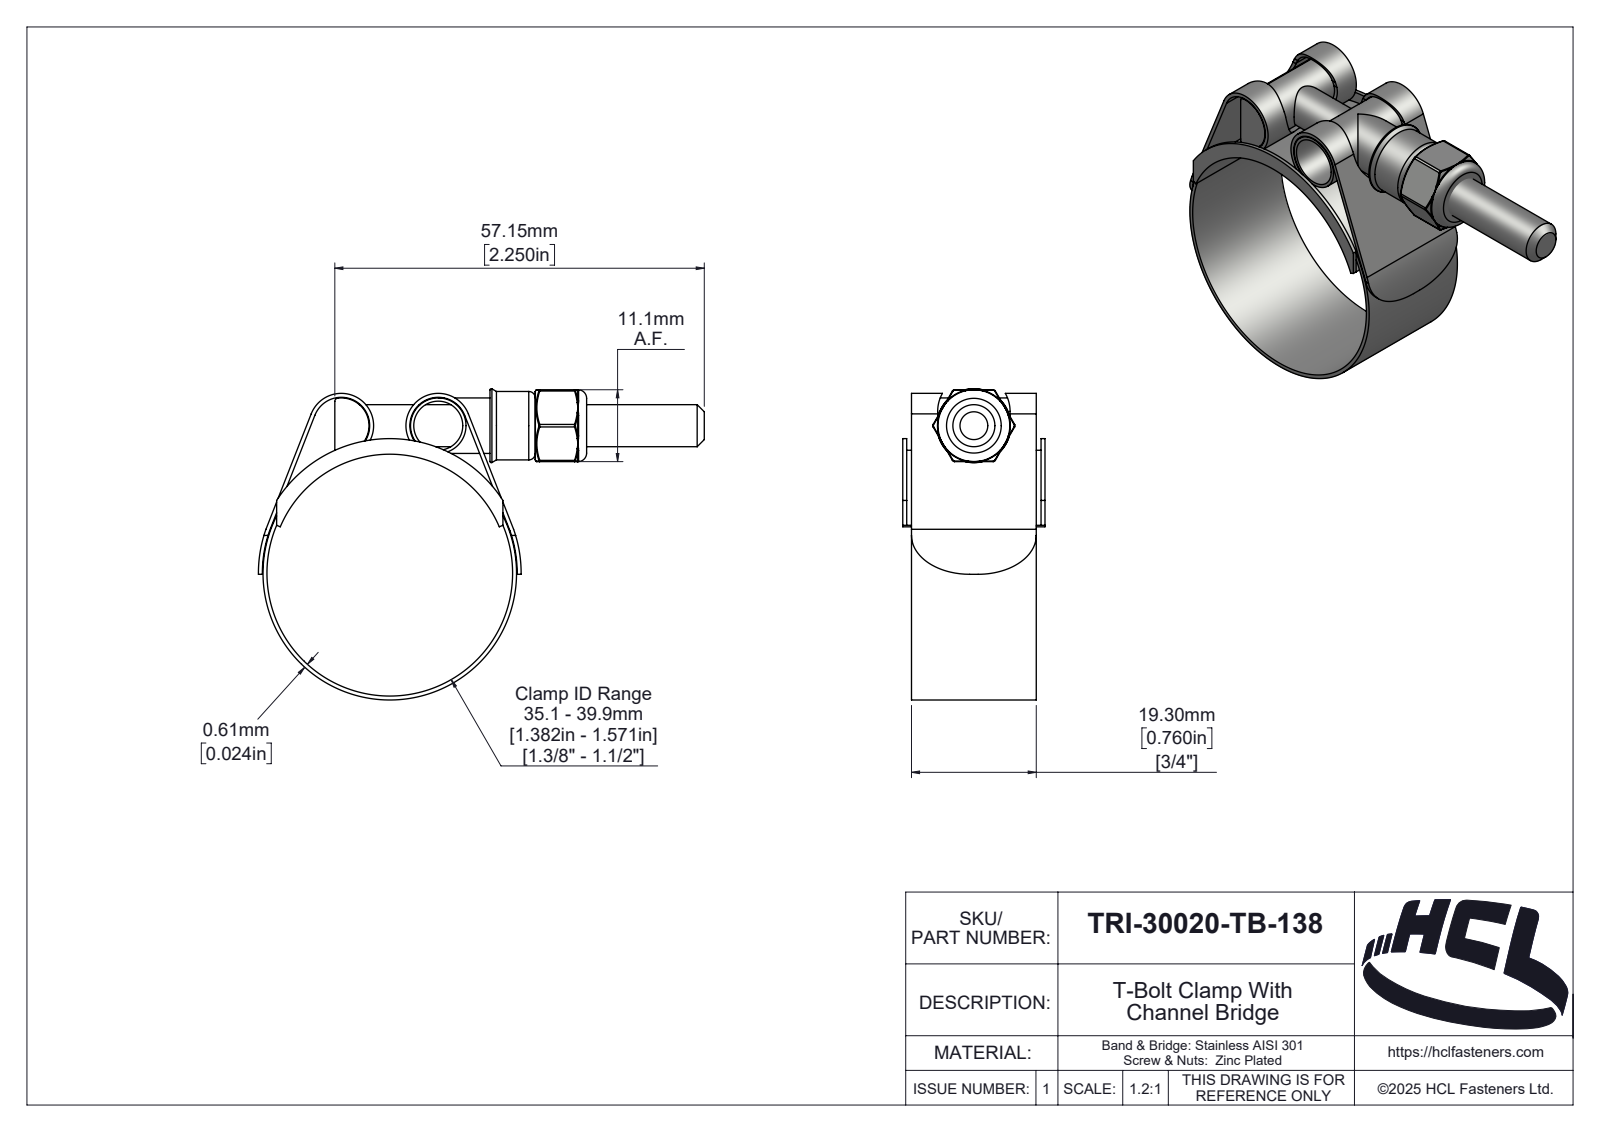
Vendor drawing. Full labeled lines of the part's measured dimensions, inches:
Part name (STEP PRODUCT): TRI-30020-TB-138
STEP written by: SolidWorks 2025 (AUTOMOTIVE_DESIGN)
Units: inches
Bodies: 6 solids, 340 faces (48 planar, 128 cylindrical, 164 other)
Overall size (bounding box): 2.715 × 1.895 × 0.866
Volume: 0.394 in³ · Surface area: 20.65 in²
Round holes (diameter × count): ⌀0.213 ×1, ⌀0.25 ×1, ⌀0.256 ×1, ⌀0.298 ×1, ⌀1.496 ×1
Round bosses / shafts (diameter × count): ⌀0.338 ×2, ⌀1.544 ×1, ⌀0.417 ×1
Partial cylindrical surfaces — rounded edges, fillets, slot ends (radius × count): R0.015 ×6, R0.02 ×2, R0.173 ×2, R0.197 ×2, R0.22 ×2, R0.023 ×1, R0.095 ×1, R0.119 ×1
Main face-to-face distances: 0.024, 0.029, 0.053, 0.813, 0.76, 0.842, 0.789, 0.866, 0.818, 1.22
Hole centre spacings: 0.945
